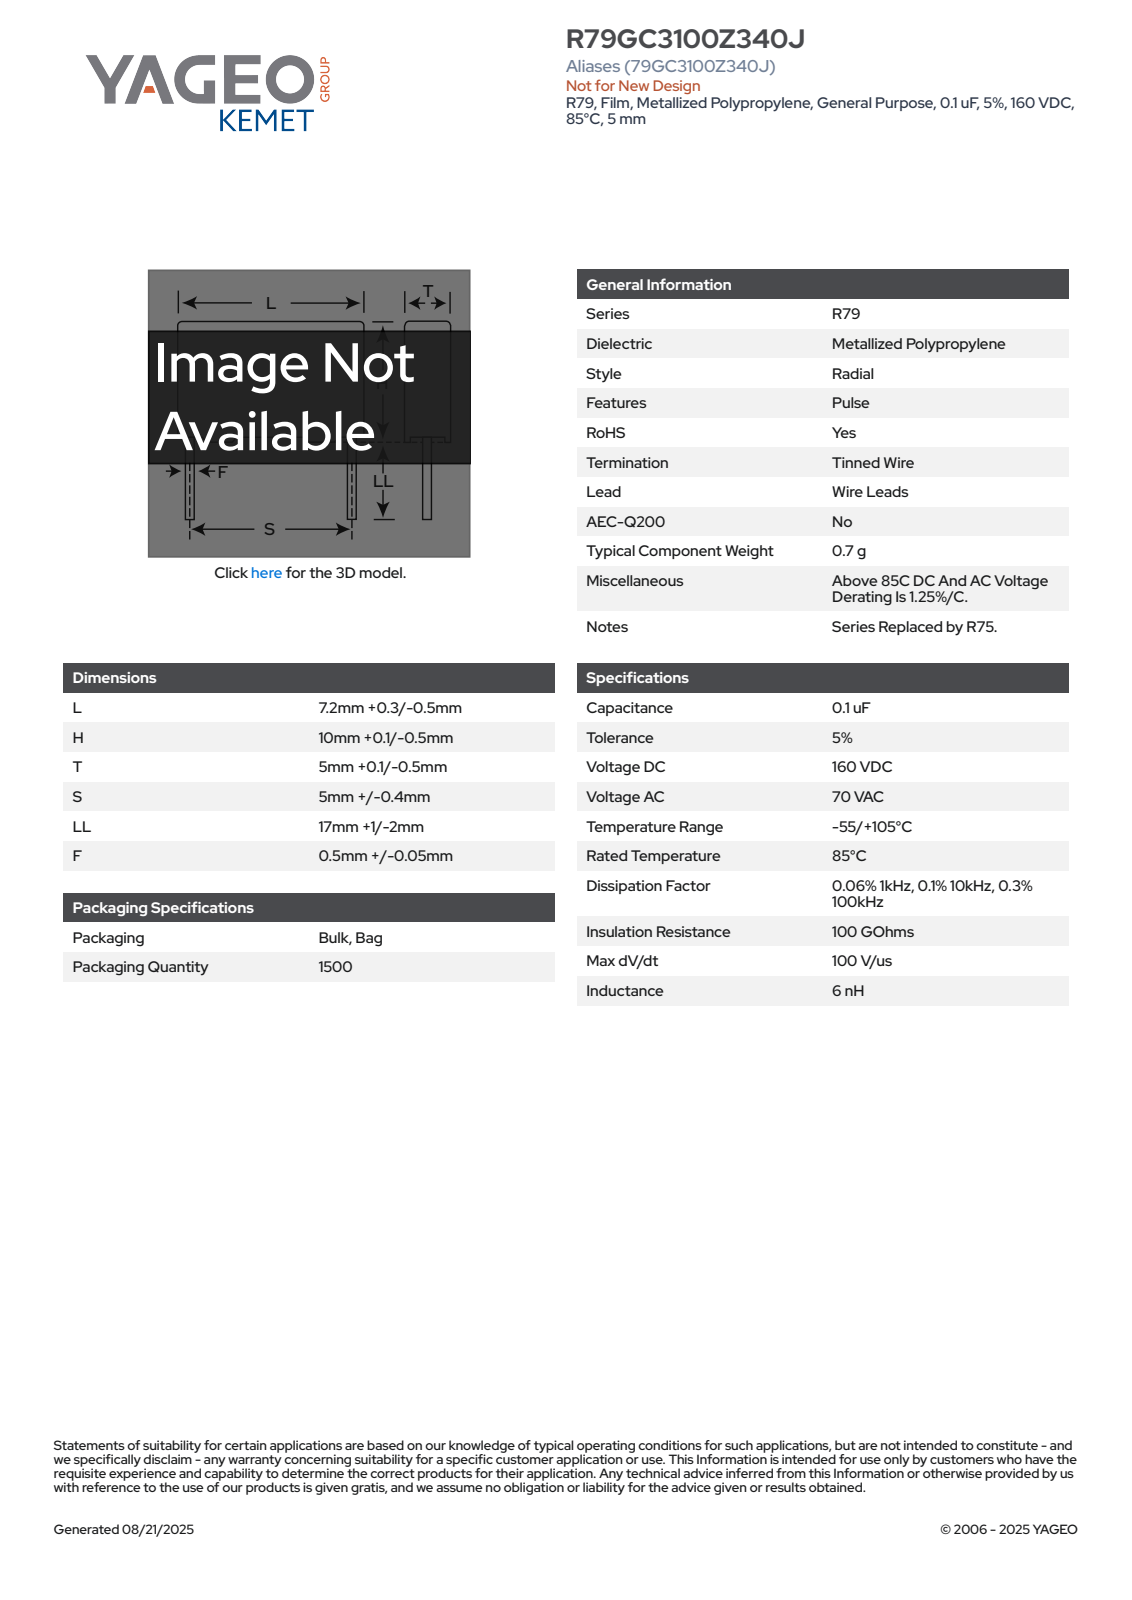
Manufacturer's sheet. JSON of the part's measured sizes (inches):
{"part_name": "CFR_RB2_7.2X10X5_L7.5H10.1T5.1S5LL18F0.55", "step_written_by": "SolidWorks 2021 (AUTOMOTIVE_DESIGN)", "units": "inches", "bodies": {"solids": 4, "faces": 85, "planar": 77, "cylindrical": 8, "other": 0}, "overall_size": [1.106, 0.295, 0.201], "volume_in3": 0.023, "surface_area_in2": 0.636, "round_bosses_or_shafts": [[0.022, 2]], "partial_cylinders_radius": [[0.02, 4]], "face_to_face_distances": [0.201, 0.295, 0.368, 0.191, 0.285, 0.03, 0.398, 0.181, 0.276, 0.014]}
